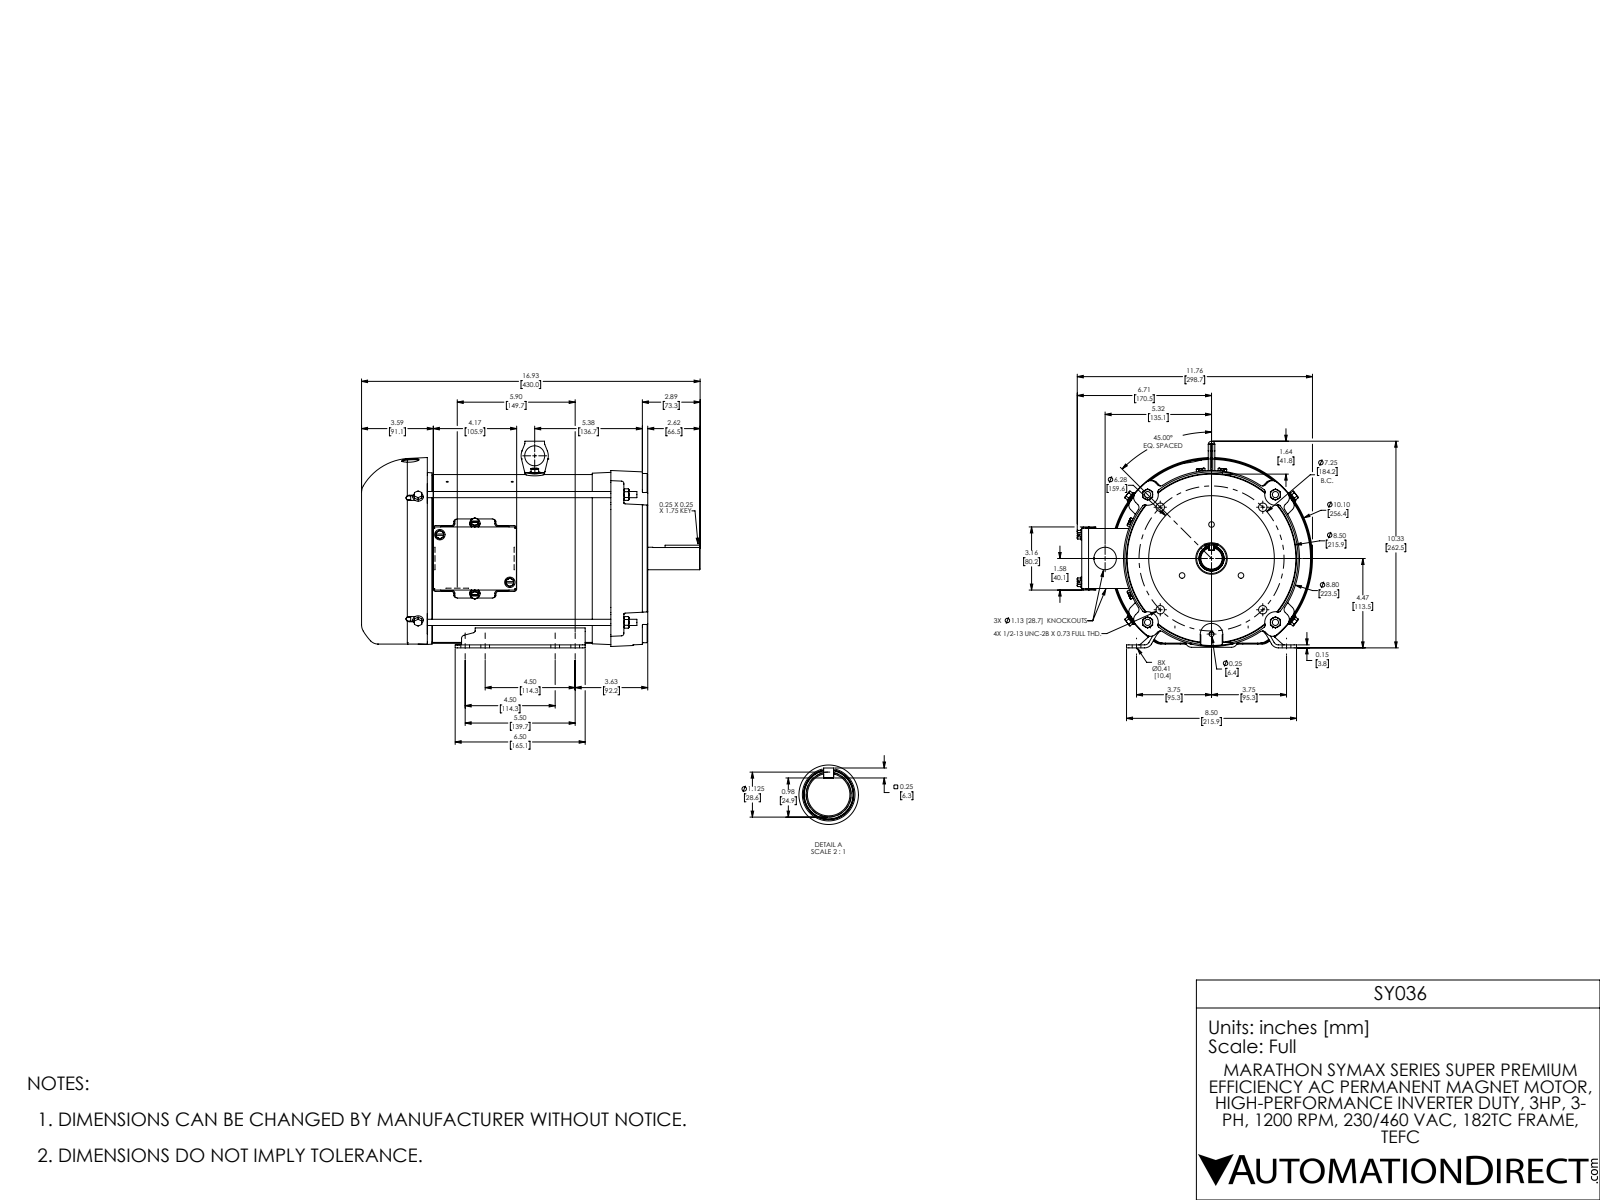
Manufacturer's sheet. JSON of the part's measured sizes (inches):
{"part_name": "036225-800_RevD_182TC_3HP Coord", "step_written_by": "SolidWorks 2017 (AUTOMOTIVE_DESIGN)", "units": "inches", "bodies": {"solids": 32, "faces": 3123, "planar": 937, "cylindrical": 926, "other": 1260}, "overall_size": [16.929, 11.761, 10.334], "volume_in3": 158.4, "surface_area_in2": 1711, "round_holes": [[0.05, 11], [0.38, 8], [0.213, 7], [0.15, 6], [0.104, 4], [0.236, 4], [0.257, 4], [0.28, 4], [0.344, 4], [0.422, 4], [0.435, 4], [0.435, 4]], "round_bosses_or_shafts": [[0.25, 10], [0.52, 6], [0.522, 4], [0.31, 4], [0.309, 2], [8.499, 1], [8.395, 1], [8.327, 1]], "partial_cylinders_radius": [[0.02, 72], [0.125, 64], [0.12, 57], [0.08, 24], [0.13, 20], [0.09, 16], [0.19, 16], [0.03, 10]], "face_to_face_distances": [0.048, 0.2, 0.15, 11.478, 11.278, 11.698, 11.498, 0.22, 12.123, 11.923], "hole_center_spacings": [5.793, 0.848, 0.893, 0.917, 1, 1.543, 3.5, 3.625]}
